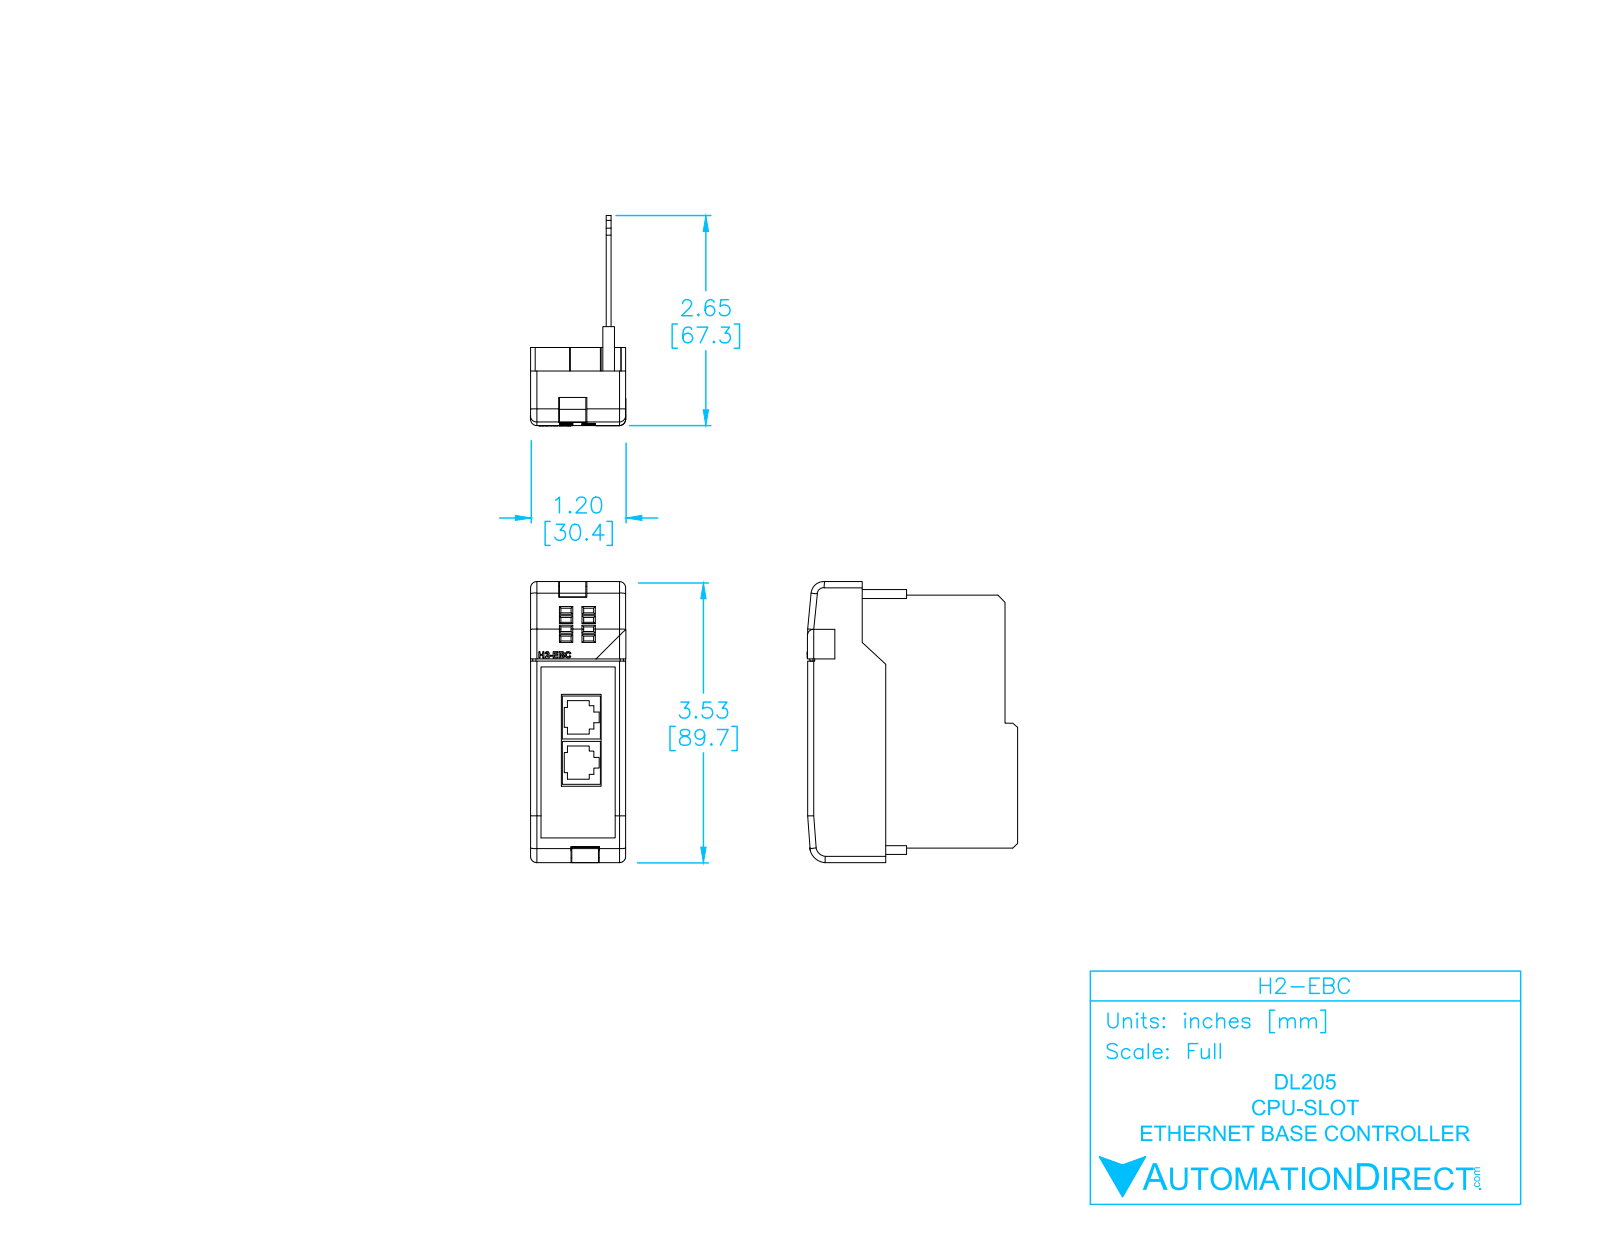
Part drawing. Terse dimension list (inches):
name: H2-EBC
written by: SolidWorks 2009 (AUTOMOTIVE_DESIGN)
unit: in
bodies: 4 solids, 393 faces (270 planar, 84 cylindrical, 39 other)
size: 3.543 × 2.653 × 1.203
volume: 1.18 in³; area: 46.16 in²
rounds: 28× R0.02, 11× R0.079, 4× R0.01, 2× R0.039, 1× R0.103, 1× R0.149, 1× R0.162, 1× R0.208
face distances: 0.059, 0.186, 0.127, 0.245, 0.956, 1.142, 0.02, 1.015, 1.201, 0.897
